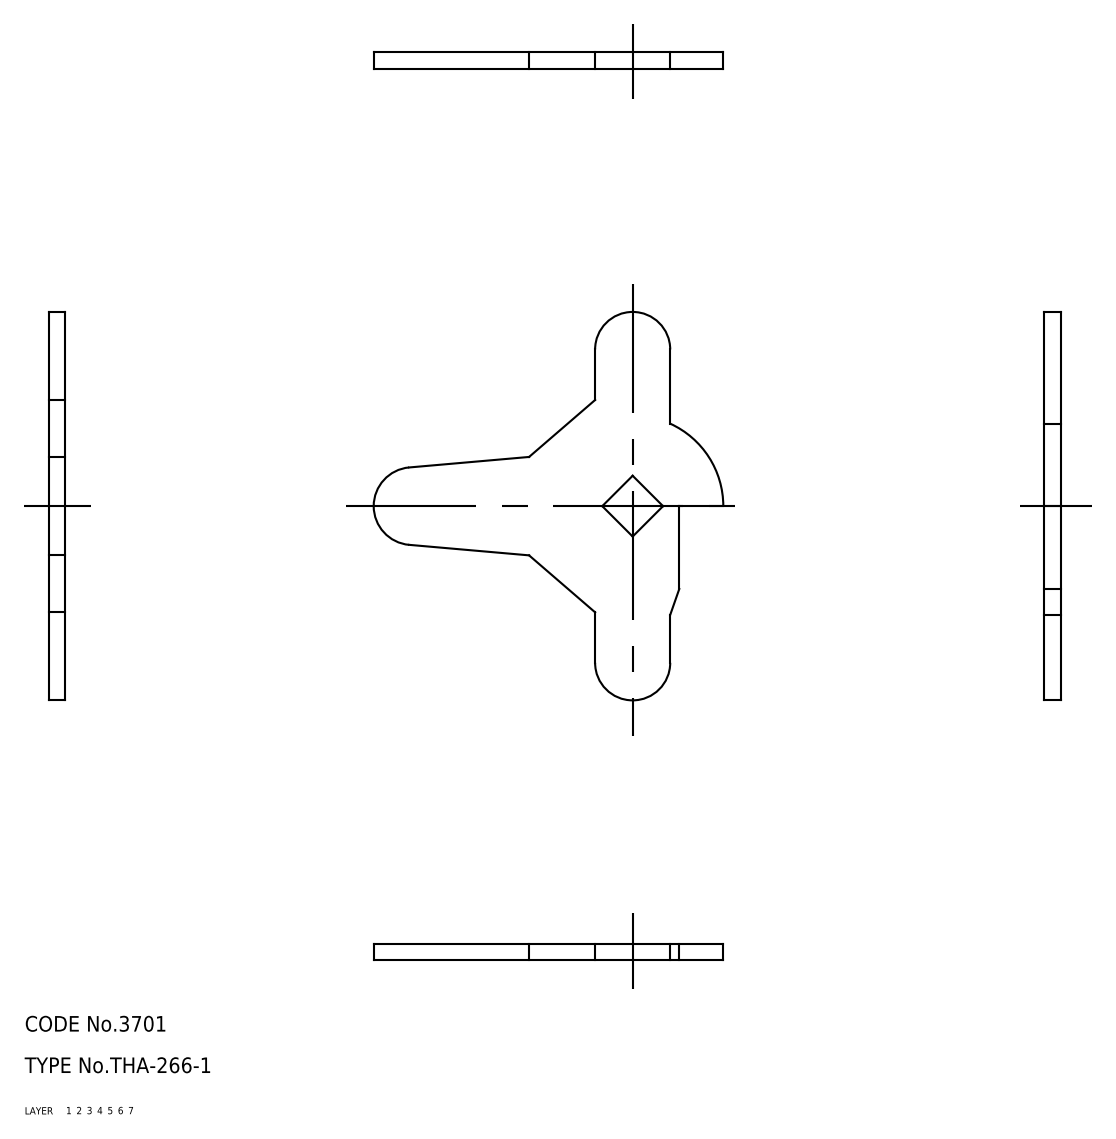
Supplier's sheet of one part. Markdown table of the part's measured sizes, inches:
| quantity | value |
| --- | --- |
| part name | cam |
| STEP written by | CADfix (AUTOMOTIVE_DESIGN) |
| units | inches |
| bodies | 1 solid, 21 faces (0 planar, 0 cylindrical, 21 other) |
| overall size | 2.953 × 2.657 × 0.126 |
| volume | 0.386 in³ |
| surface area | 7.49 in² |
